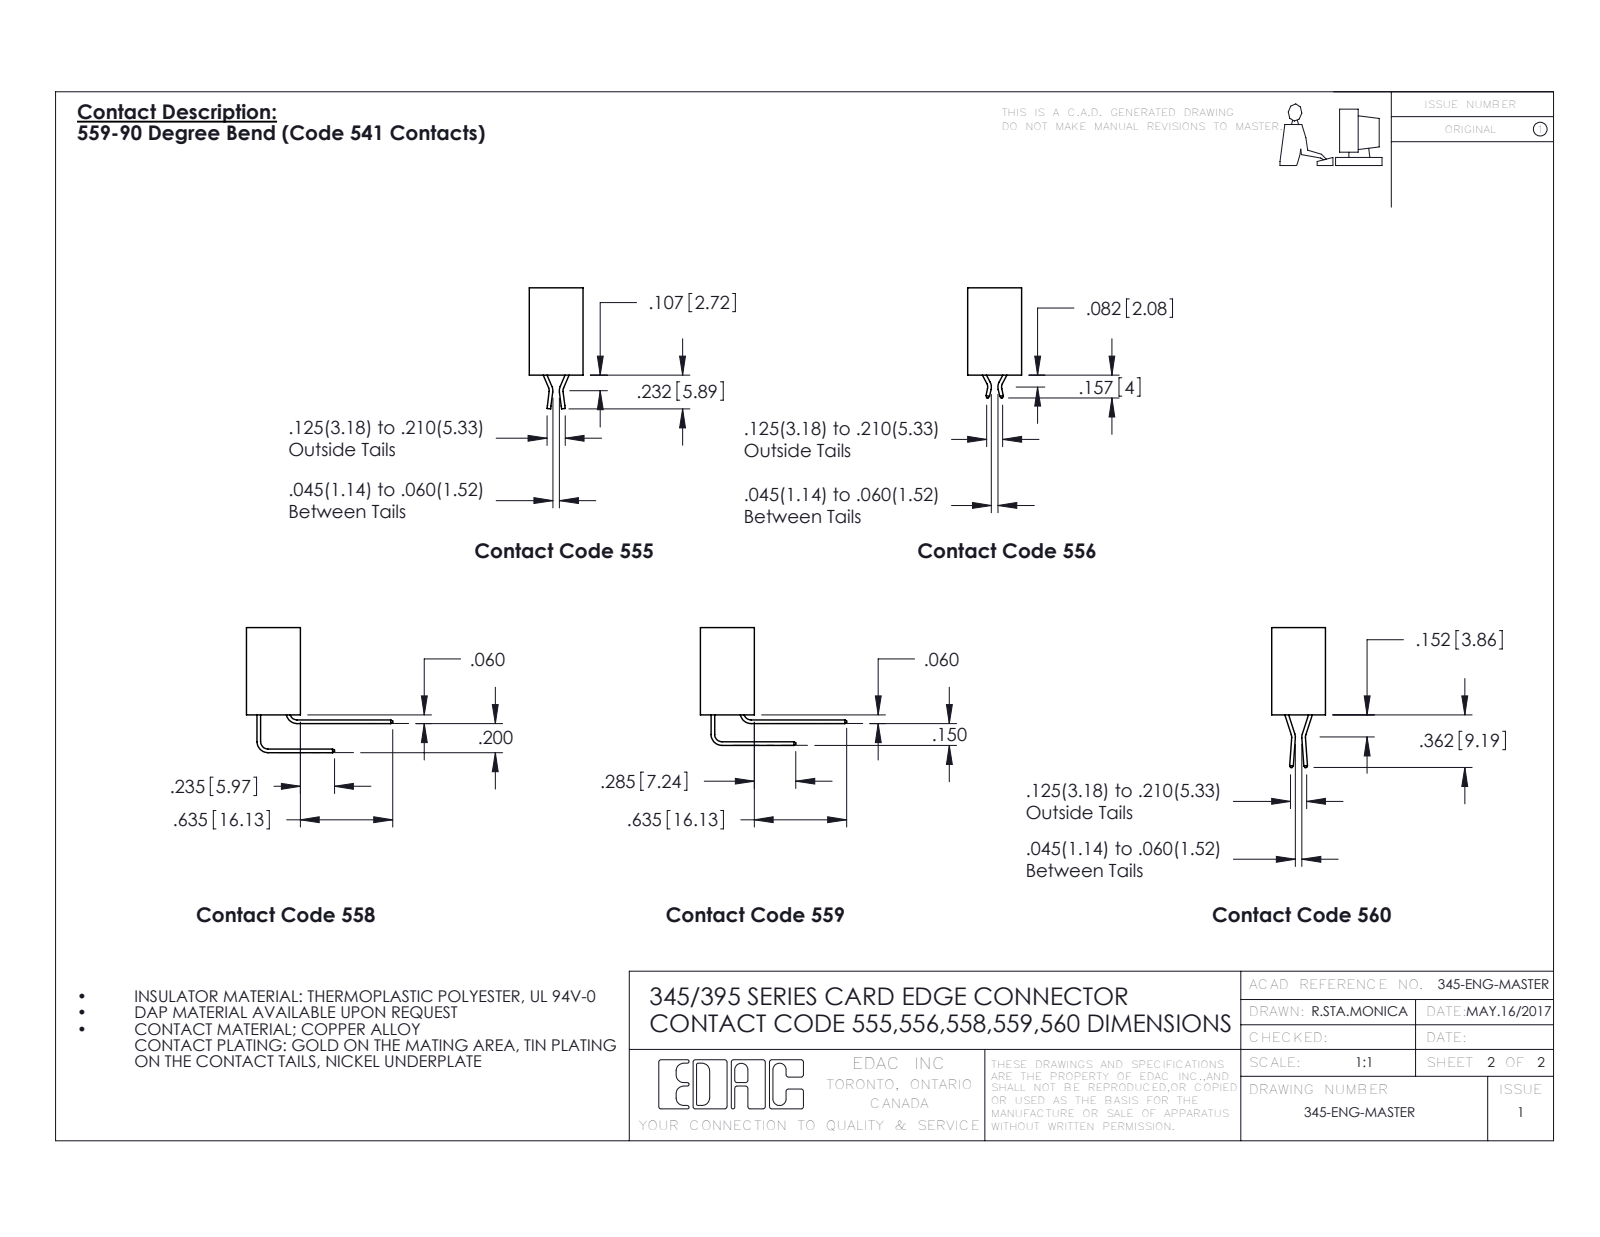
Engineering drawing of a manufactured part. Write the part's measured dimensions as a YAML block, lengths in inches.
part_name: "395-020-558-112; 345 Part_Flush Mounting Lugs - Side Mount; 345-292-001_558 Tail - 2"
step_written_by: "SolidWorks 2016 (CONFIG_CONTROL_DESIGN)"
units: inches
bodies: {solids: 21, faces: 1326, planar: 920, cylindrical: 406, other: 0}
overall_size: [2.835, 0.859, 0.605]
volume: 0.405
surface_area: 13.6
round_holes:
  - {diameter: 0.128, count: 2}
  - {diameter: 0.064, count: 1}
partial_cylinders:
  - {radius: 0.006, count: 40}
  - {radius: 0.01, count: 22}
  - {radius: 0.007, count: 6}
  - {radius: 0.031, count: 6}
  - {radius: 0.026, count: 3}
  - {radius: 0.031, count: 2}
  - {radius: 0.04, count: 2}
  - {radius: 0.014, count: 1}
face_to_face_distances: [0.298, 0.072, 0.2, 0.37, 0.098, 0.272, 0.025, 0.225, 0.149, 0.6]
hole_center_spacings: [2.575]
